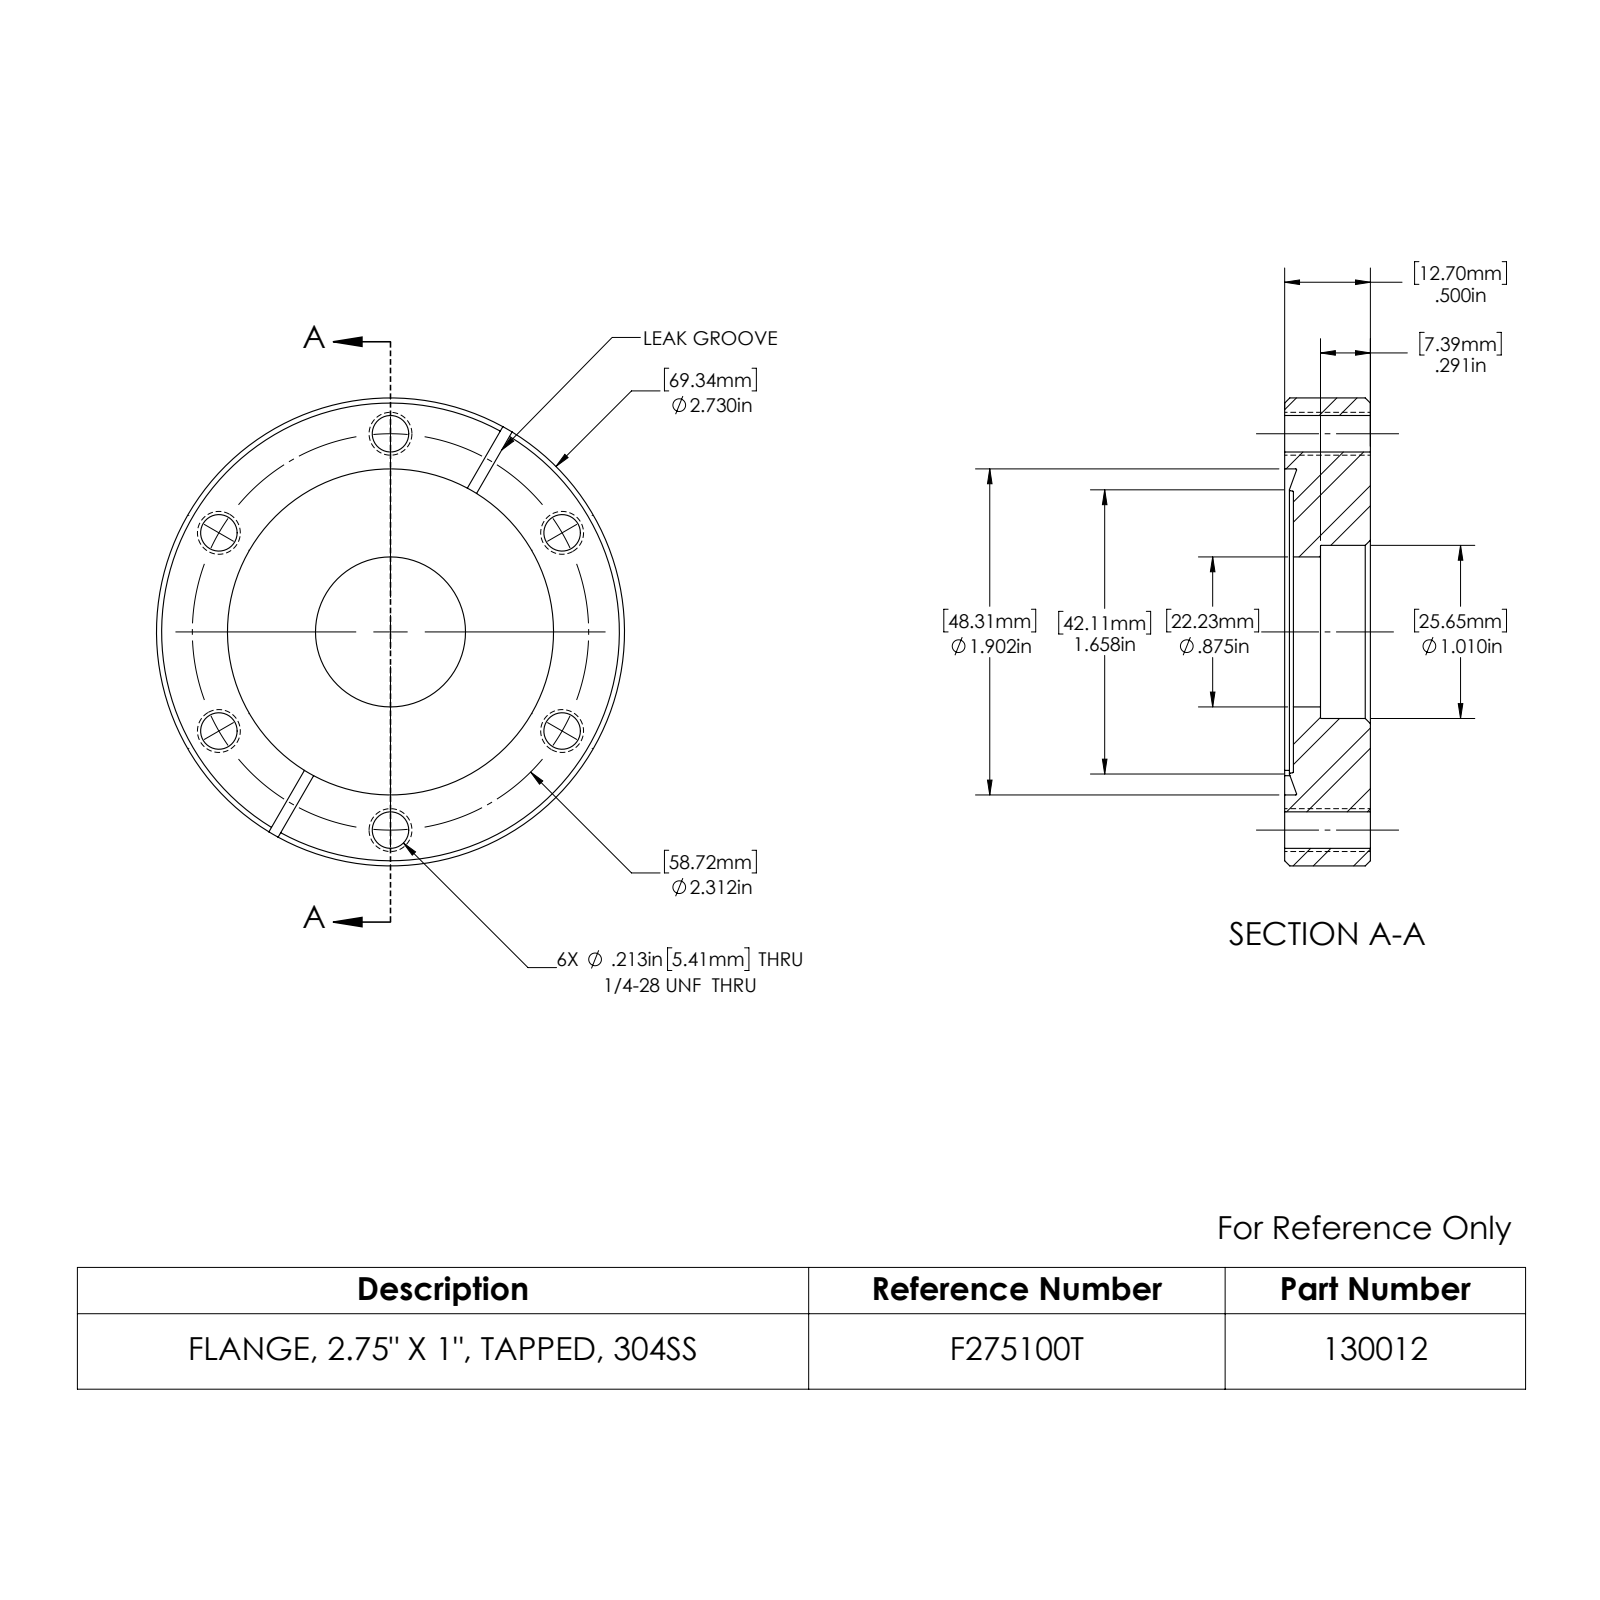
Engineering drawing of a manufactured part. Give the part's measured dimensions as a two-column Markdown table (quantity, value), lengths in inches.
| quantity | value |
| --- | --- |
| part name | 130012_D |
| STEP written by | SolidWorks 2022 (CONFIG_CONTROL_DESIGN) |
| units | inches |
| bodies | 1 solid, 50 faces (11 planar, 20 cylindrical, 19 other) |
| overall size | 2.73 × 2.73 × 0.5 |
| volume | 2.336 in³ |
| surface area | 17.98 in² |
| round holes (diameter × count) | 0.213 × 6, 0.875 × 1, 1.01 × 1, 1.902 × 1 |
| round bosses / shafts (diameter × count) | 2.73 × 1 |
| main face-to-face distances | 0.5, 0.051, 0.449, 0.209, 0.158, 0.291, 0.062, 0.147, 0.438, 0.062 |
| hole center spacings | 1.156, 2.002, 2.002, 2.312, 2.312 |
